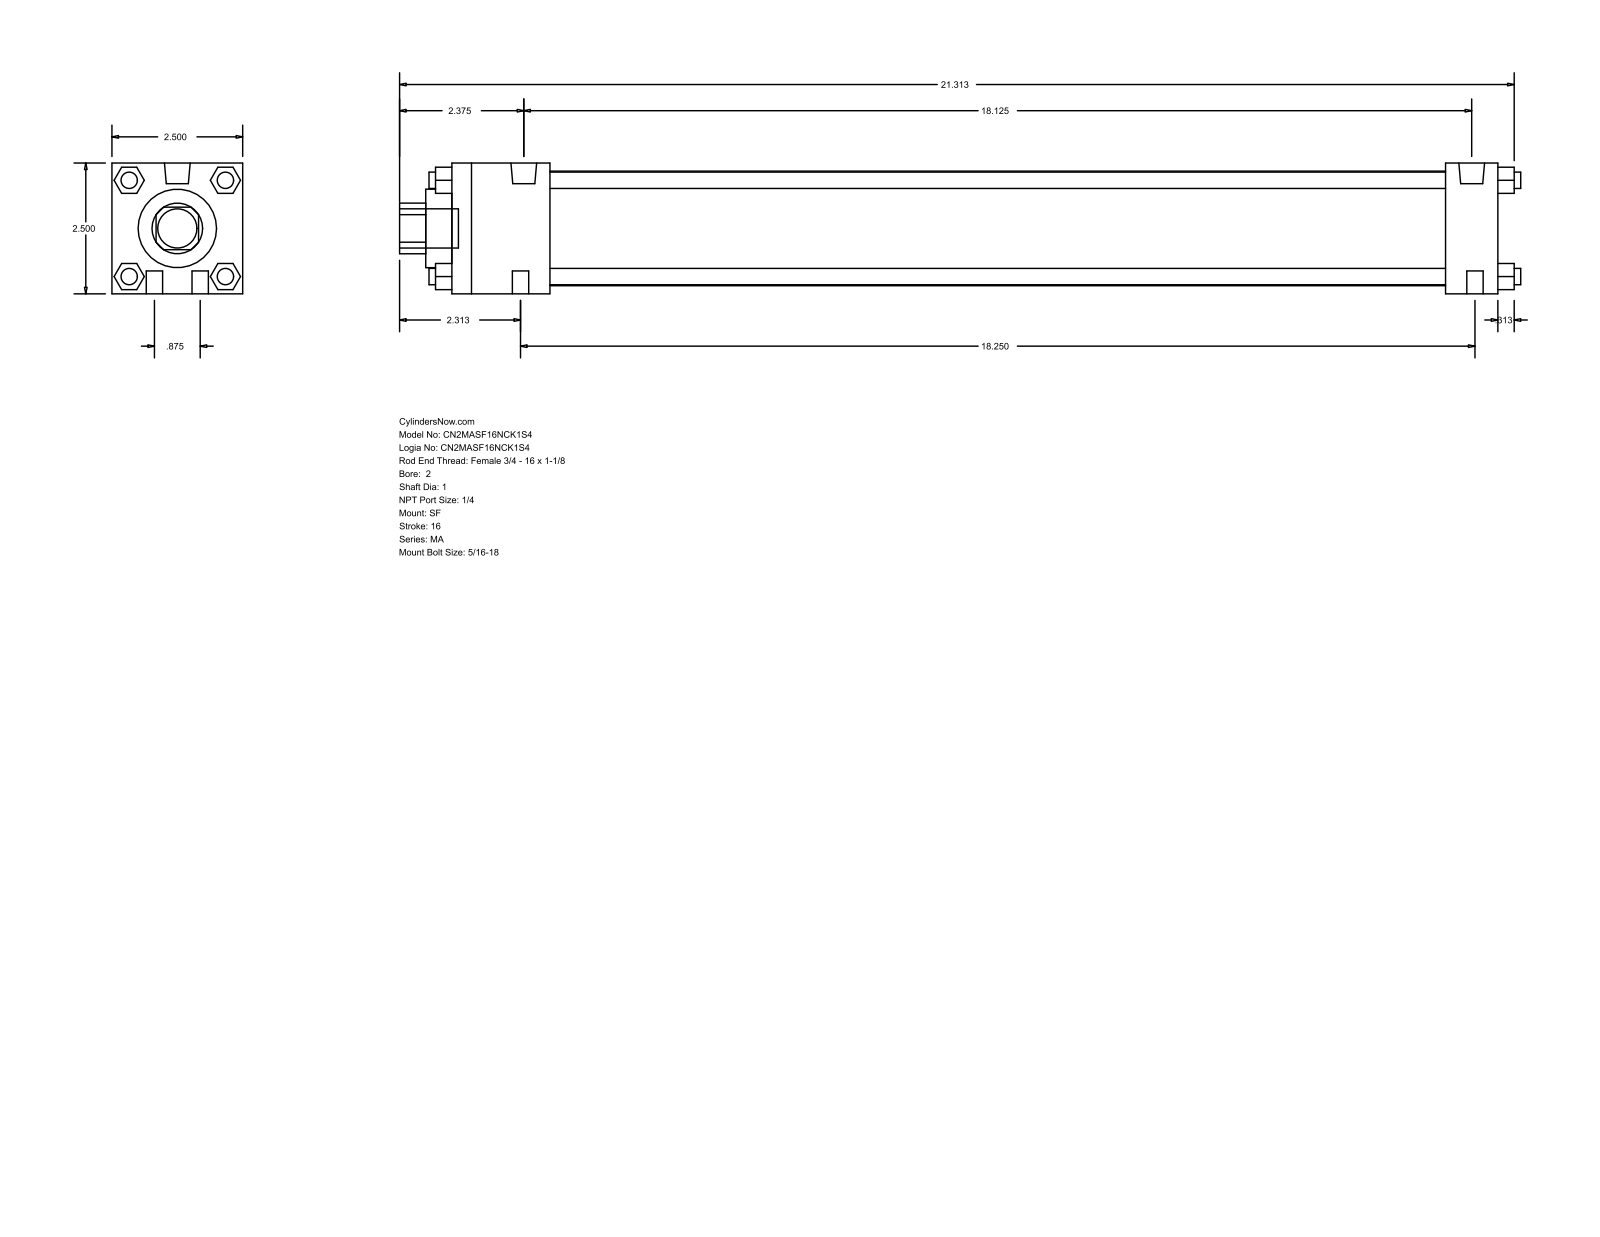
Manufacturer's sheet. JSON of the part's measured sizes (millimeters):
{"part_name": "MA_SF__0200_1", "step_written_by": "GSSL Pune (CONFIG_CONTROL_DESIGN)", "units": "millimeters", "bodies": {"solids": 0, "faces": 124, "planar": 94, "cylindrical": 30, "other": 0}, "overall_size": [544.51, 63.5, 63.5], "round_holes": [[25.4, 1], [38.1, 1], [55.63, 1]], "round_bosses_or_shafts": [[7.94, 10], [12.49, 2], [19.05, 1]], "partial_cylinders_radius": [[12.29, 1]], "face_to_face_distances": [63.5, 508, 12.7, 25.4, 482.6, 47.63, 434.97, 460.37, 23.37, 40.47]}
